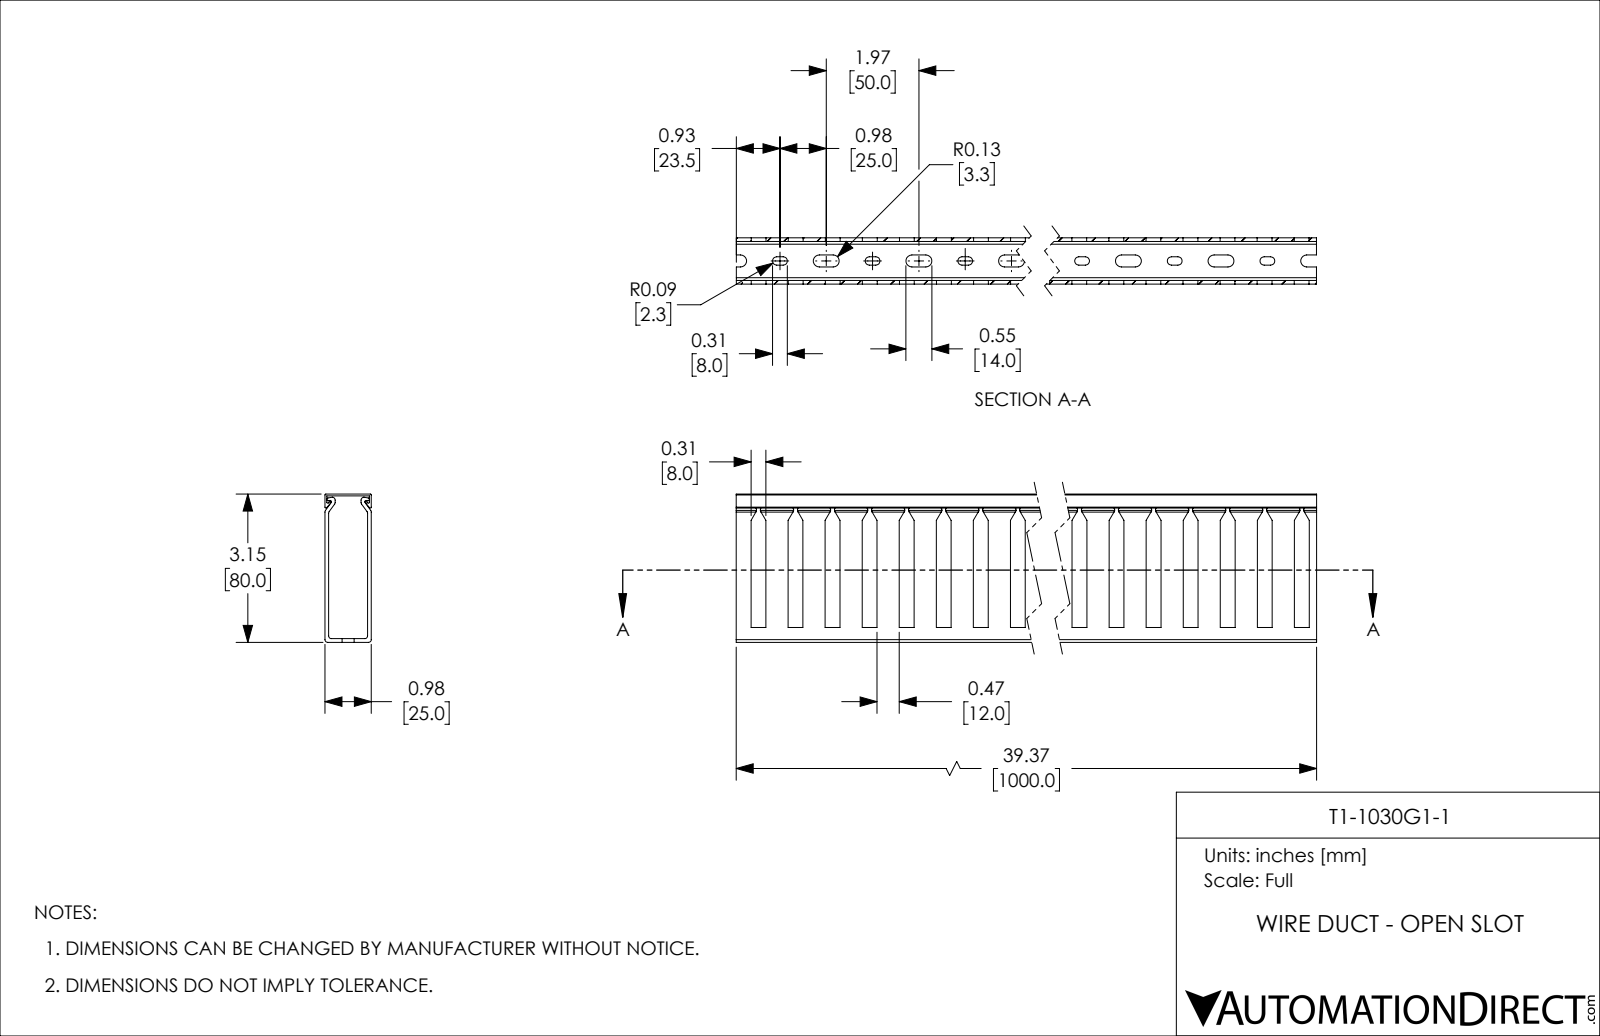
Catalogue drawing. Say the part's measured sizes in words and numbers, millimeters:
The part is named "T1-1030G1-1". Its 3-D file was written by "SolidWorks 2021 (CONFIG_CONTROL_DESIGN)". It is 2 solids with 745 faces: 434 planar, 311 cylindrical and 0 other. Overall it measures 1000 by 80 by 25 millimeters. Its volume is 384 135 cubic millimeters and its surface area 434 378 square millimeters. Partial cylindrical surfaces (rounded edges, fillets, slot ends): 40 of radius 2.25, 40 of radius 3.25, 12 of radius 1.5, 8 of radius 0.5, 6 of radius 0.75. The main face-to-face distances are 2, 23, 25, 21, 1, 80, 79, 77, 78, 24.
